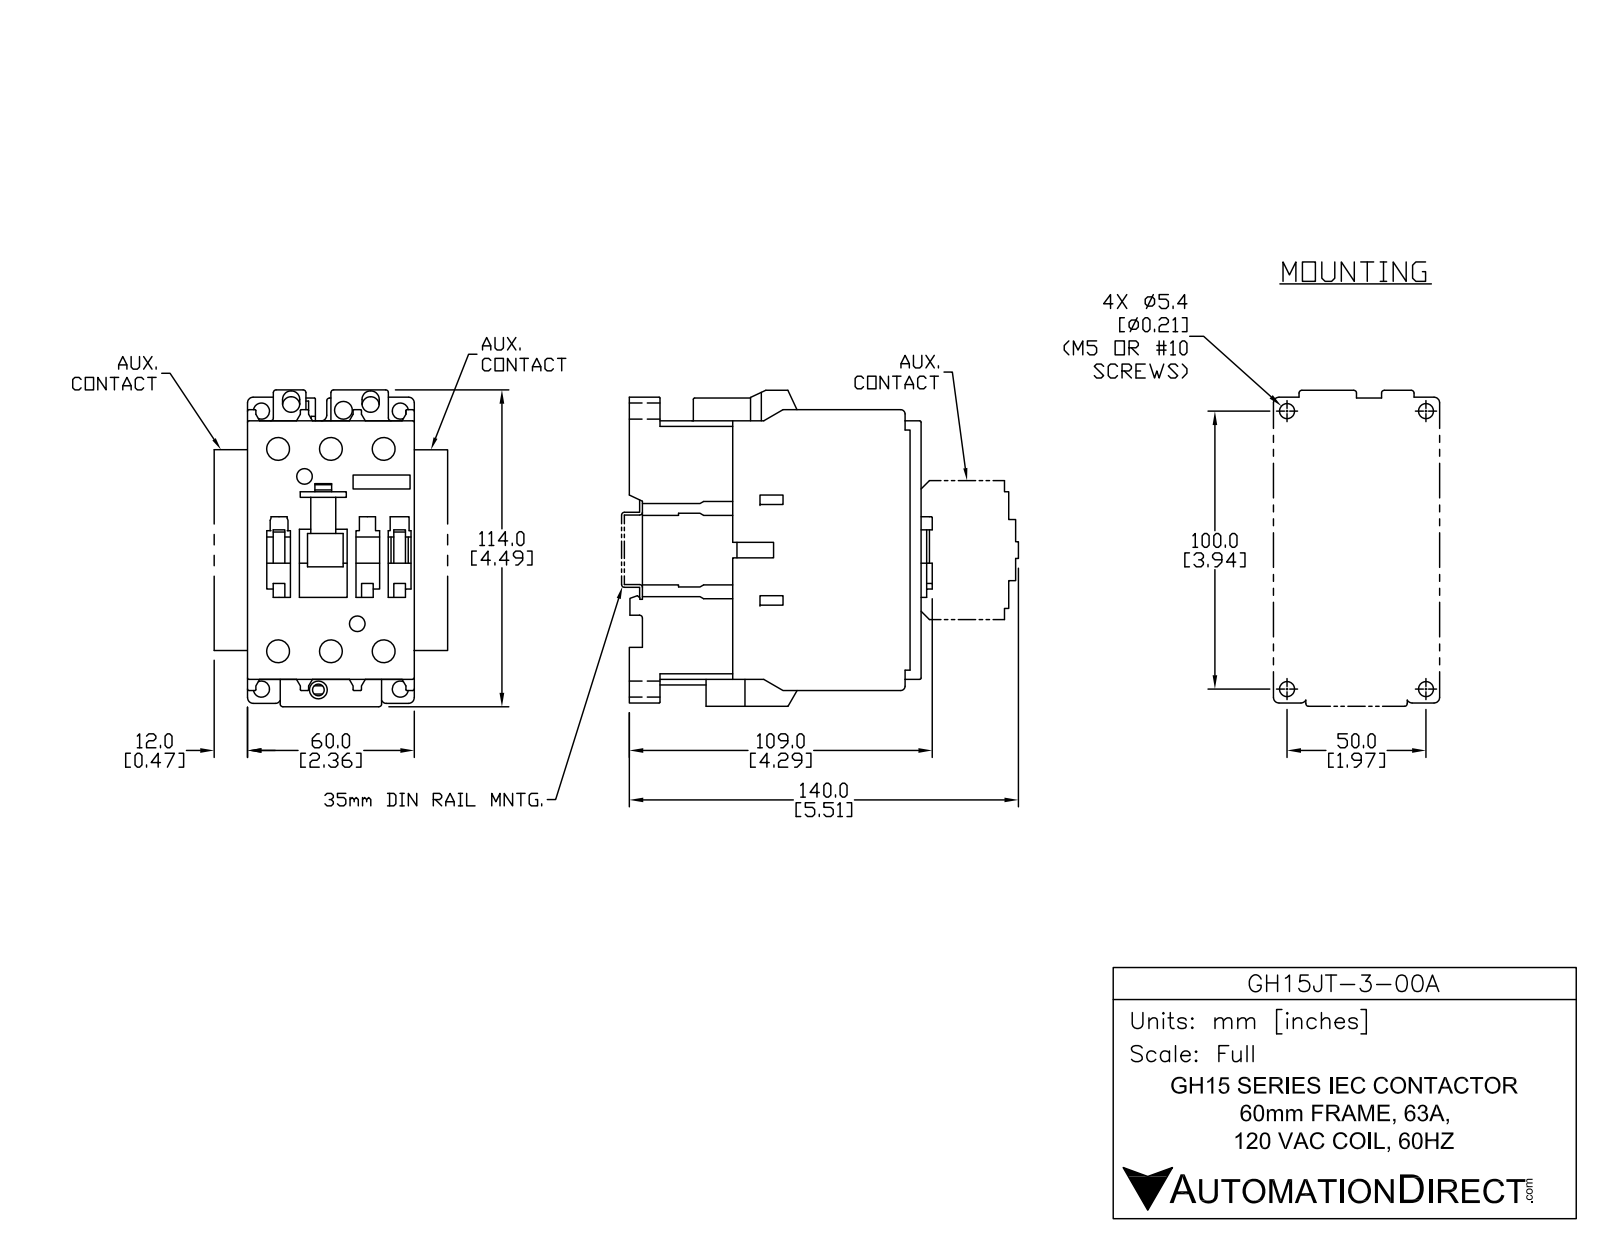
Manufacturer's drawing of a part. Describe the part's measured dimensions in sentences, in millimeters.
The part is named "GH15JT-3-00A". Its 3-D file was written by "SolidWorks 2009 (AUTOMOTIVE_DESIGN)". It is 1 solid with 836 faces: 632 planar, 40 cylindrical and 164 other. Overall it measures 114 by 109.75 by 60 millimeters. Its volume is 561 052 cubic millimeters and its surface area 67 816 square millimeters. Round holes: 6 of diameter 8.5, 4 of diameter 6, 1 of diameter 5, 1 of diameter 6.14, 1 of diameter 6.5. Partial cylindrical surfaces (rounded edges, fillets, slot ends): 10 of radius 2, 2 of radius 1.23, 2 of radius 1.25. The main face-to-face distances are 60, 19, 99.5, 93, 10.5, 38, 8.5, 5, 20.5, 67.25. The hole center spacings are 89.8, 15, 19, 28.53, 46.1, 74.95, 86.46, 96.82.
